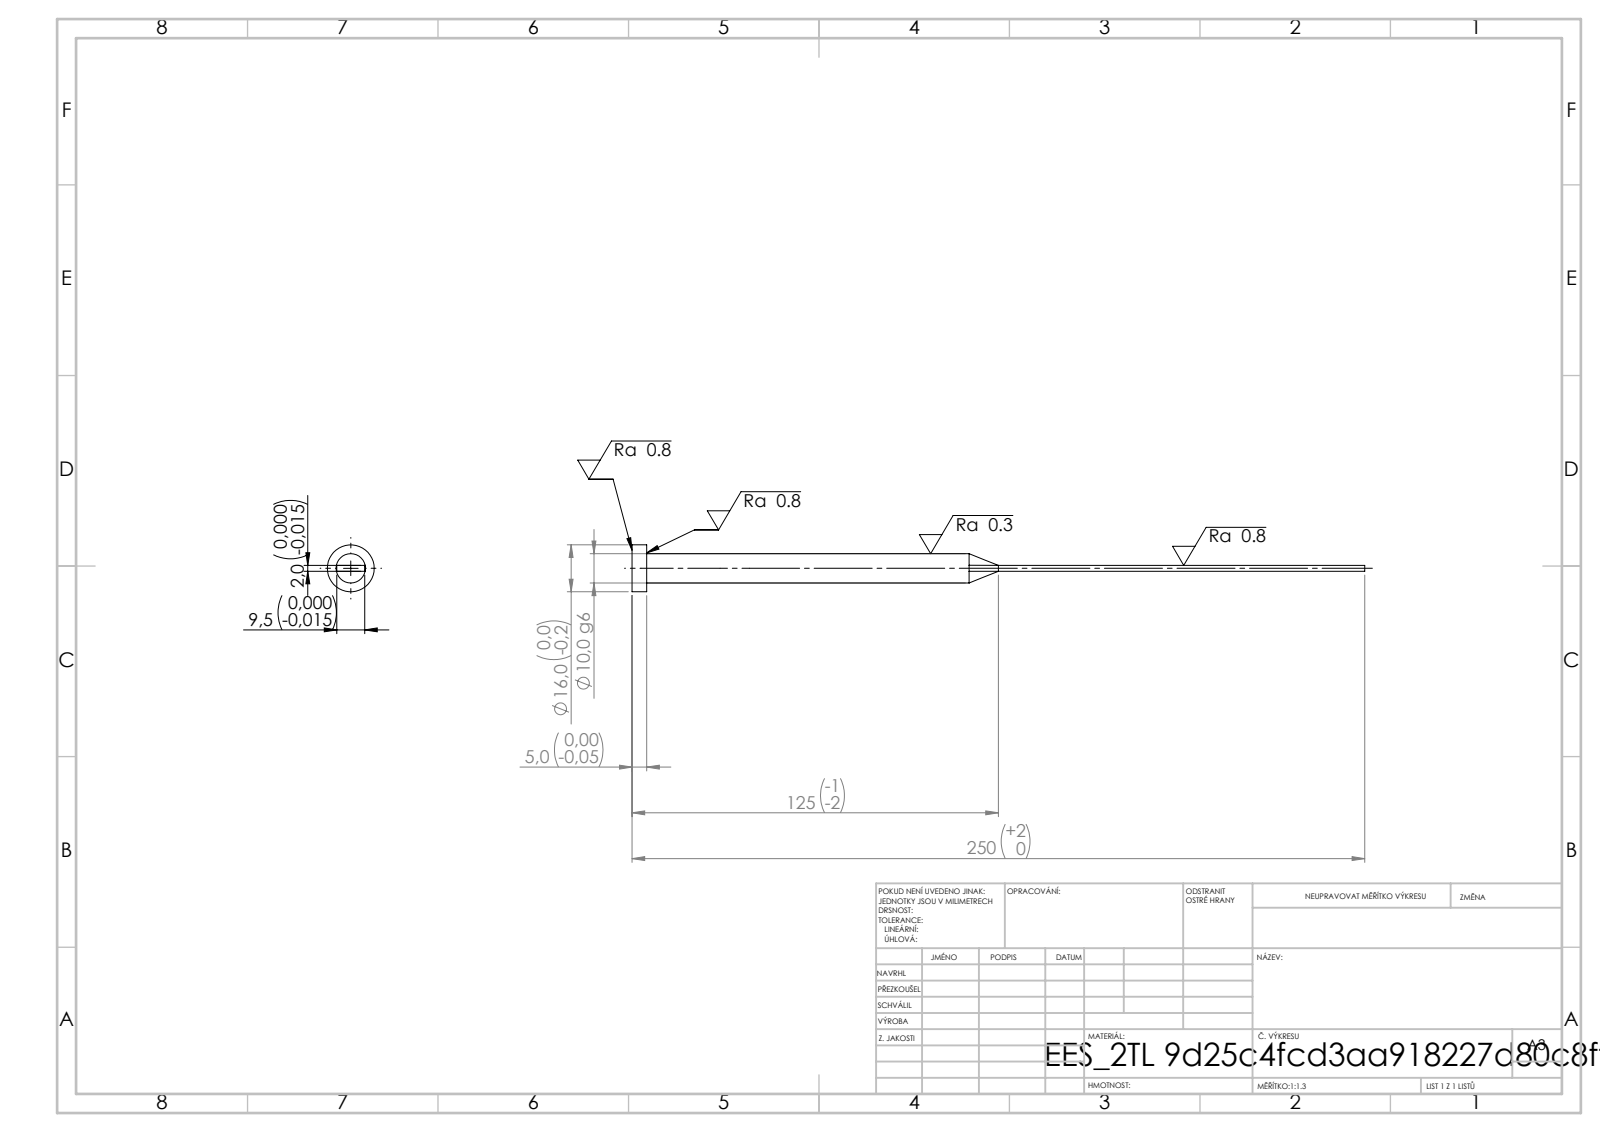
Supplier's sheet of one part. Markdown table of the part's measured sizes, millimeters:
| quantity | value |
| --- | --- |
| STEP written by | SolidWorks 2019 (CONFIG_CONTROL_DESIGN) |
| units | millimeters |
| bodies | 1 solid, 15 faces (7 planar, 4 cylindrical, 4 other) |
| overall size | 250 × 16 × 16 |
| volume | 12 486 mm³ |
| surface area | 7 194 mm² |
| round bosses / shafts (diameter × count) | 16 × 1, 10 × 1 |
| main face-to-face distances | 2, 9.5, 5, 250, 245 |
